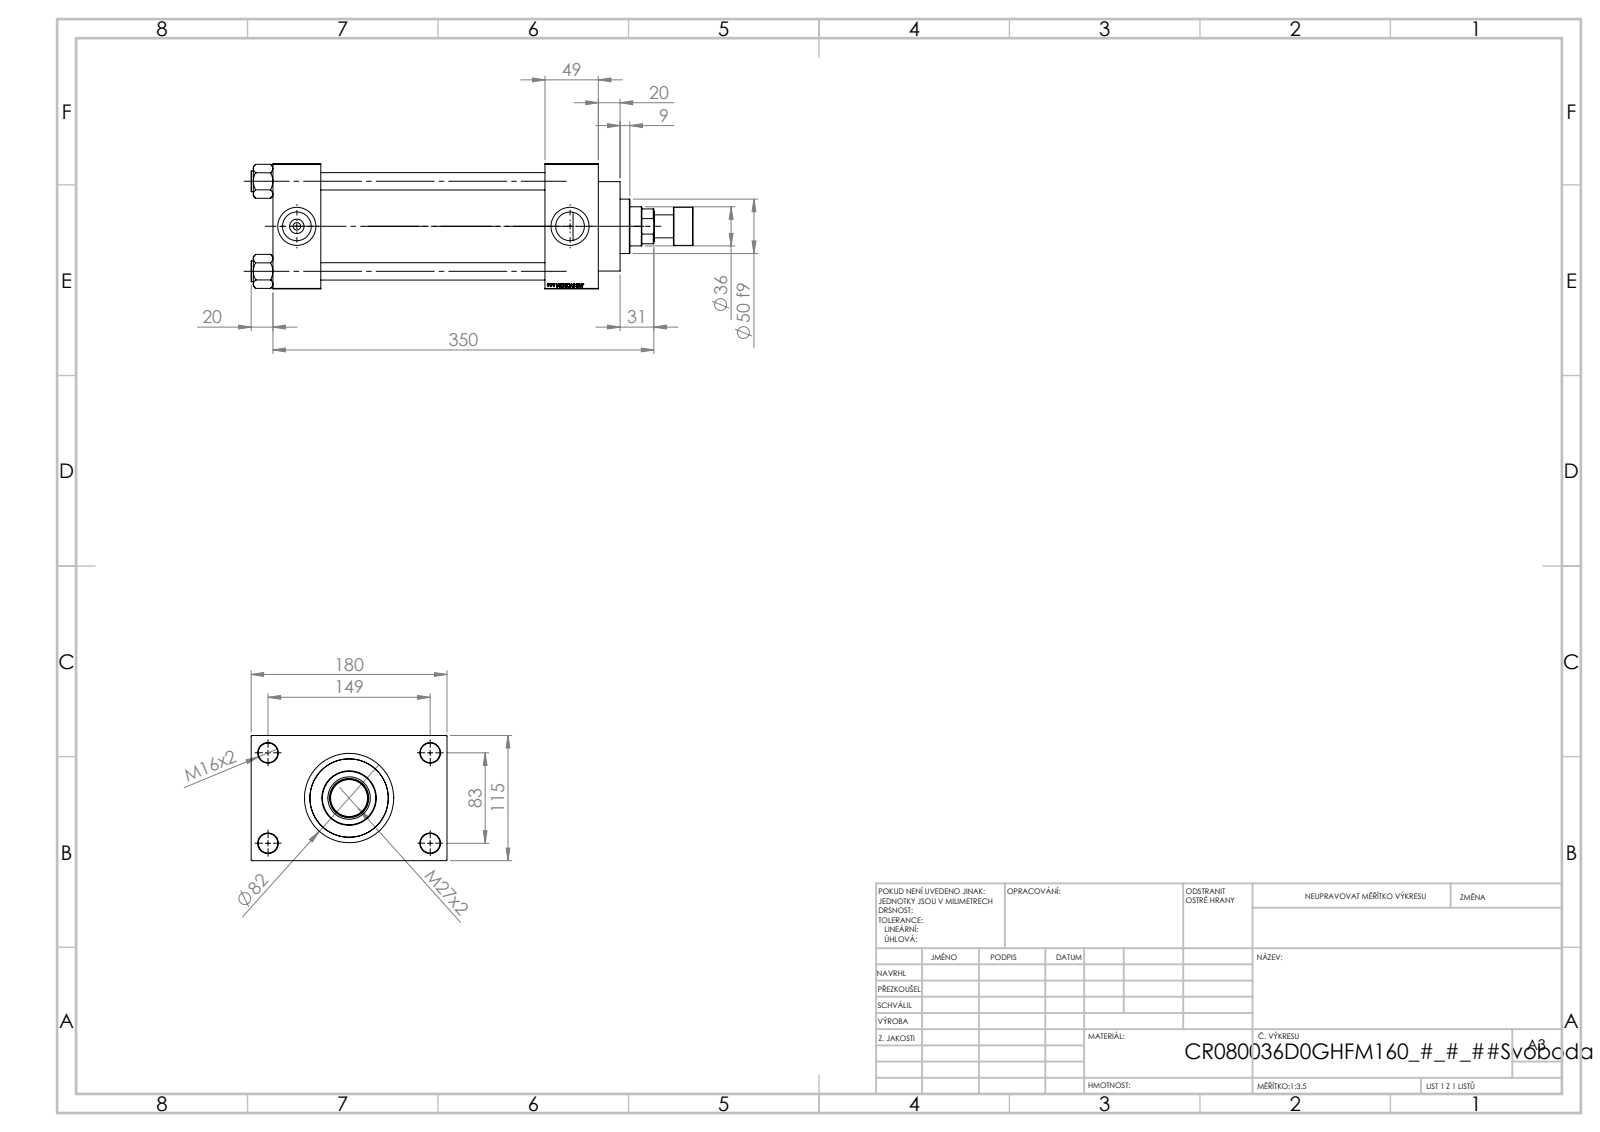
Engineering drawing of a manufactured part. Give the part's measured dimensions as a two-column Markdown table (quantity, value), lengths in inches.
| quantity | value |
| --- | --- |
| part name | V215CR_D_TYCINKA; V215CR_VCP_D; V215CR_D_Body; V215CR_ROD_END_F (+2 more) |
| STEP written by | SolidWorks 2019 (CONFIG_CONTROL_DESIGN) |
| units | inches |
| bodies | 12 solids, 1165 faces (549 planar, 92 cylindrical, 524 other) |
| overall size | 15.984 × 7.087 × 4.528 |
| volume | 144.5 in³ |
| surface area | 649.7 in² |
| round holes (diameter × count) | 0.63 × 4, 0.709 × 4, 0.276 × 2, 1.041 × 2, 1.378 × 2, 1.004 × 1, 1.417 × 1, 1.535 × 1, 2.402 × 1, 2.835 × 1, 3.15 × 1 |
| round bosses / shafts (diameter × count) | 0.748 × 4, 3.386 × 1, 3.228 × 1, 1.969 × 1, 1.378 × 1, 0.827 × 1 |
| main face-to-face distances | 4.528, 8.11, 1.929, 10.039, 1.732, 9.843, 11.772, 1.28, 5.807, 7.087 |
| hole center spacings | 1.305, 2.302, 3.256, 3.357, 3.513, 4.561, 5.607, 3.268 |
